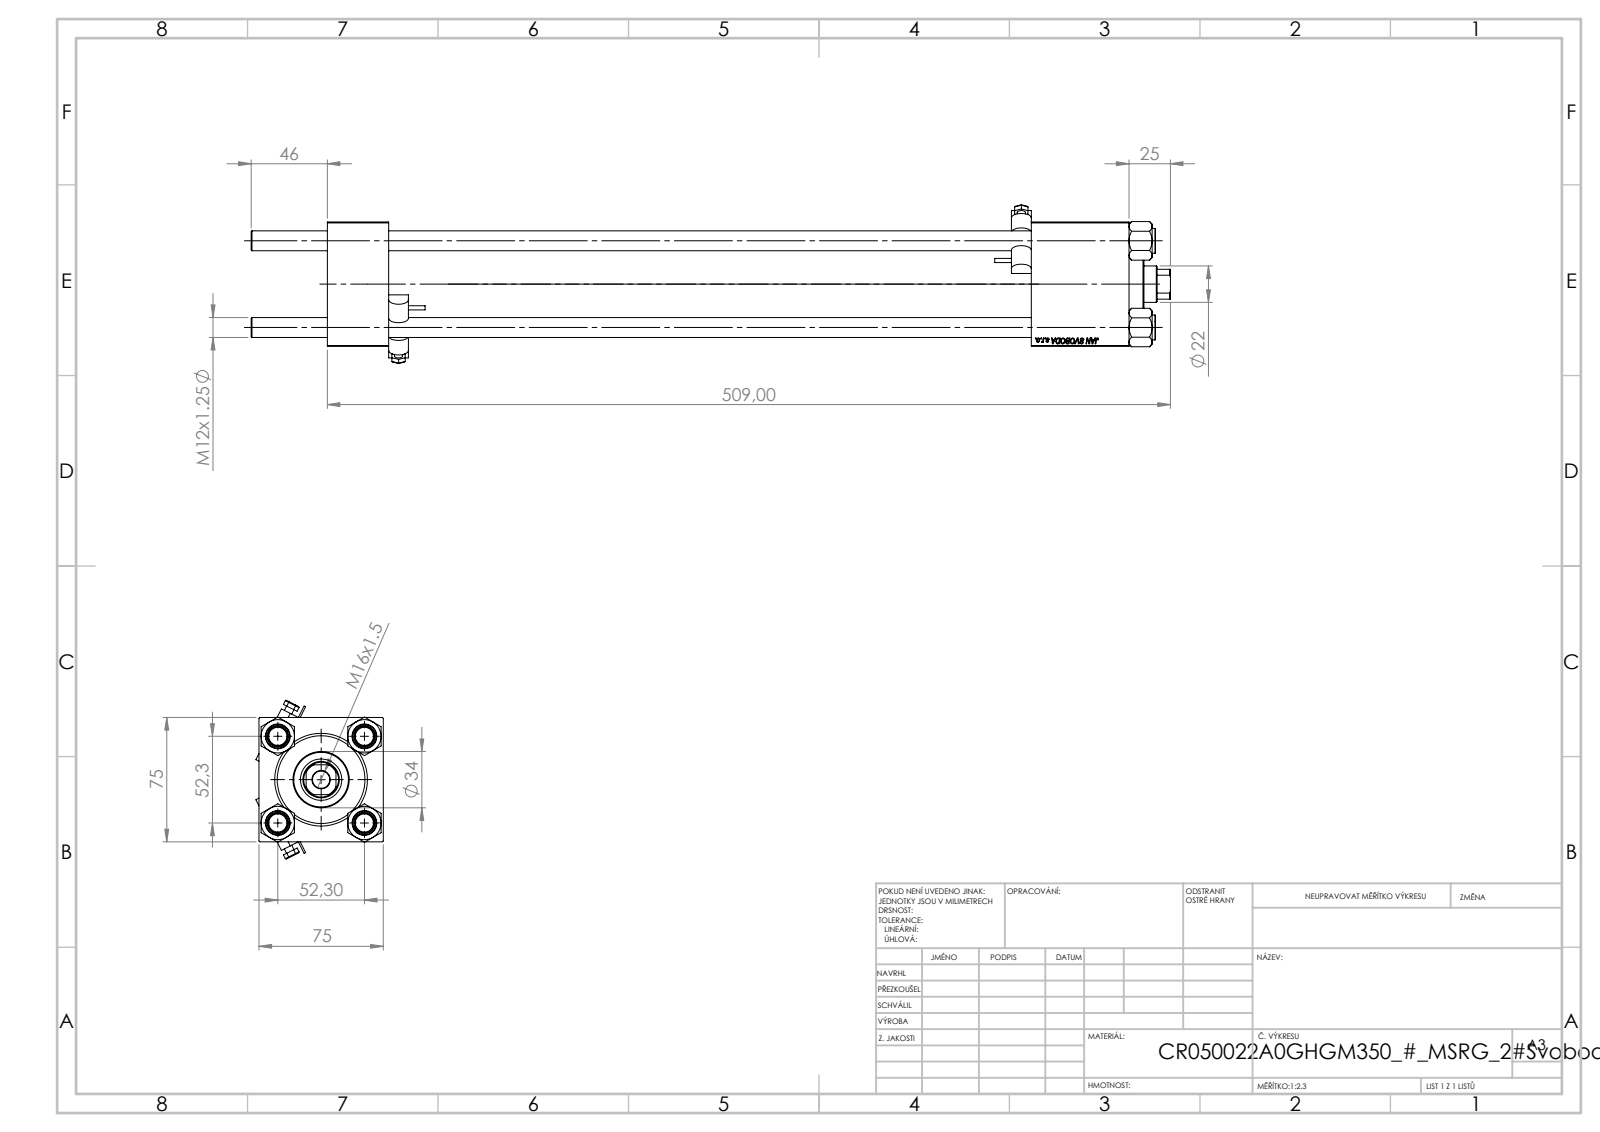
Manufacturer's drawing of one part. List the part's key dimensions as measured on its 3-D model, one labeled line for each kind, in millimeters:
Part name (STEP PRODUCT): NUT_M5; MSRF_MSRG1; CR025_012_A_0_G_A_G_M_020_+#_##_TYCINKA; V215_VC_A (+2 more)
STEP written by: SolidWorks 2019 (CONFIG_CONTROL_DESIGN)
Units: millimetres
Bodies: 13 solids, 1198 faces (556 planar, 106 cylindrical, 536 other)
Overall size (bounding box): 555 × 95.81 × 76.88
Volume: 1 137 000 mm³ · Surface area: 350 700 mm²
Round holes (diameter × count): ⌀12 ×4, ⌀7 ×2, ⌀20.96 ×2, ⌀30 ×2, ⌀10.5 ×1, ⌀22 ×1, ⌀25 ×1, ⌀41 ×1, ⌀50 ×1, ⌀53 ×1
Round bosses / shafts (diameter × count): ⌀15 ×4, ⌀5 ×2, ⌀2.5 ×2, ⌀56 ×1, ⌀34 ×1
Partial cylindrical surfaces — rounded edges, fillets, slot ends (radius × count): R0.5 ×12, R6 ×4, R10.5 ×1
Main face-to-face distances: 75, 37, 484, 447, 425, 388, 59, 455.3, 418.3, 30.3
Hole centre spacings: 36.98, 52.3, 73.96, 423.5
